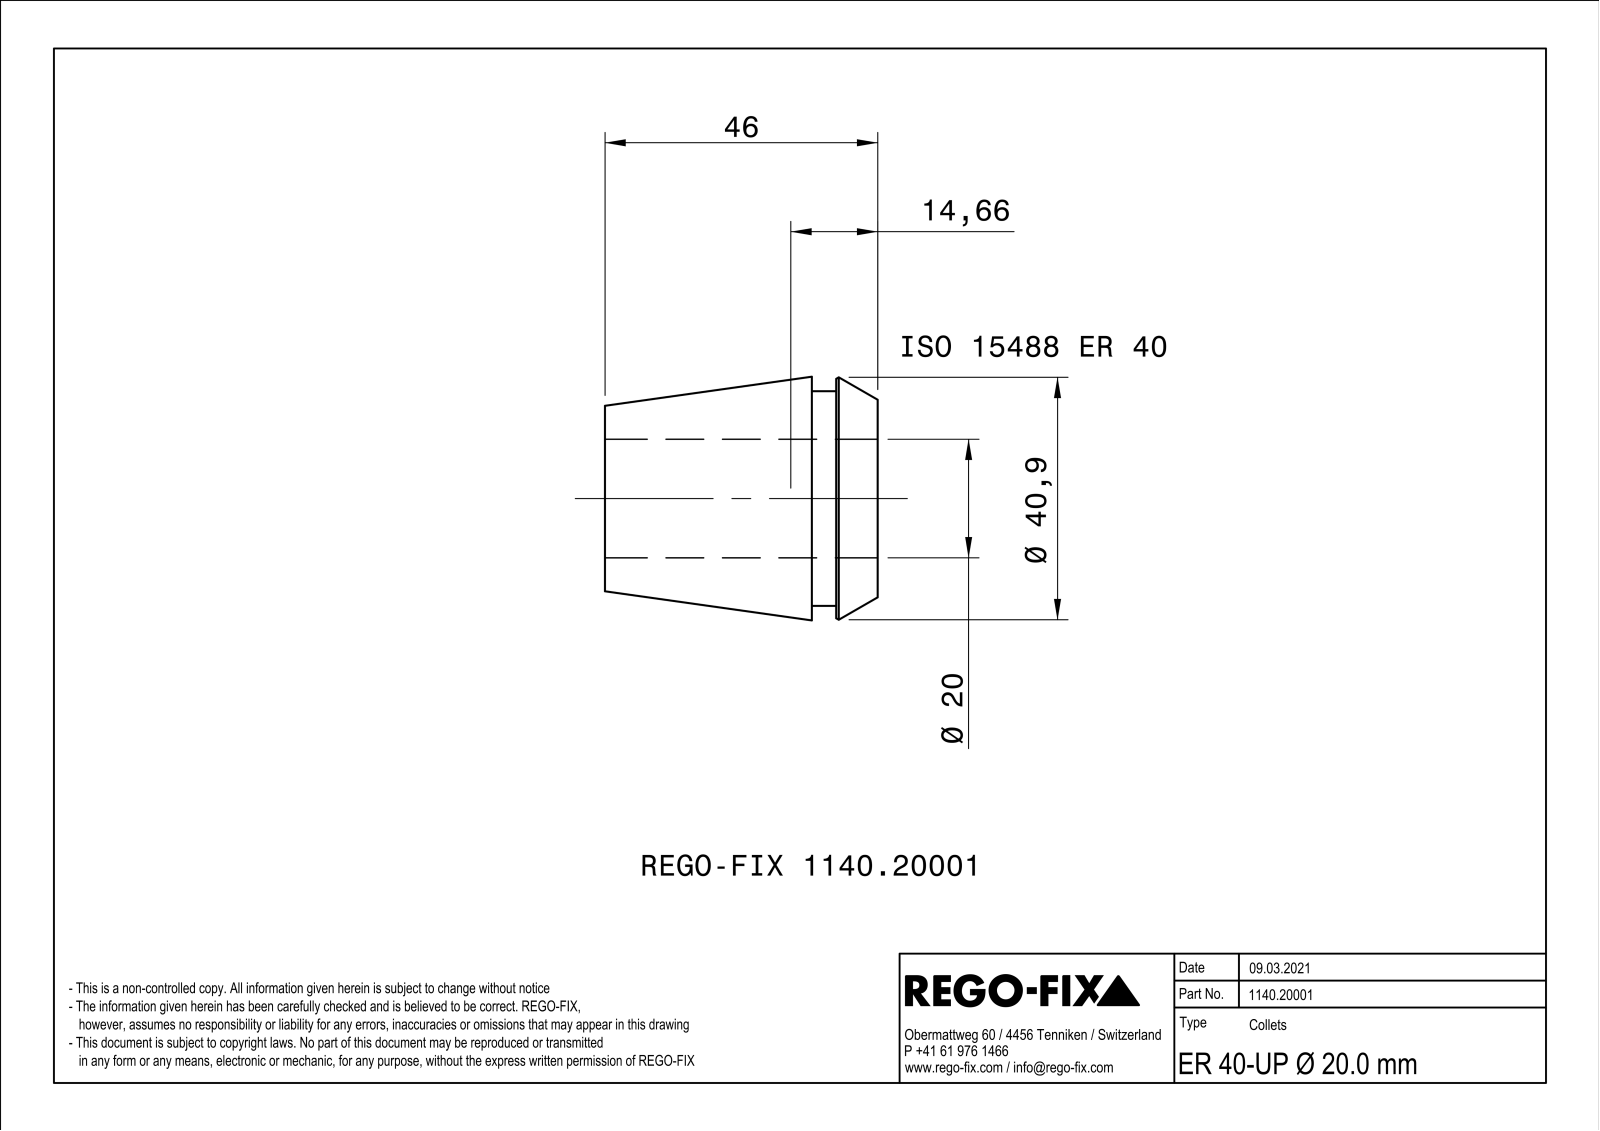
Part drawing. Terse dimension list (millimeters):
name: NOCUT
written by: SIEMENS PLM Software Solid Edge ST10 (AUTOMOTIVE_DESIGN)
unit: mm
bodies: 1 solid, 177 faces (88 planar, 9 cylindrical, 80 other)
size: 46 × 40.99 × 40.99
volume: 28 067 mm³; area: 19 083 mm²
holes: 1× ⌀20
bosses: 1× ⌀36.2
face distances: 1, 46, 11.1, 34.9, 7, 4.1, 39, 7.5, 0.5, 3.6
